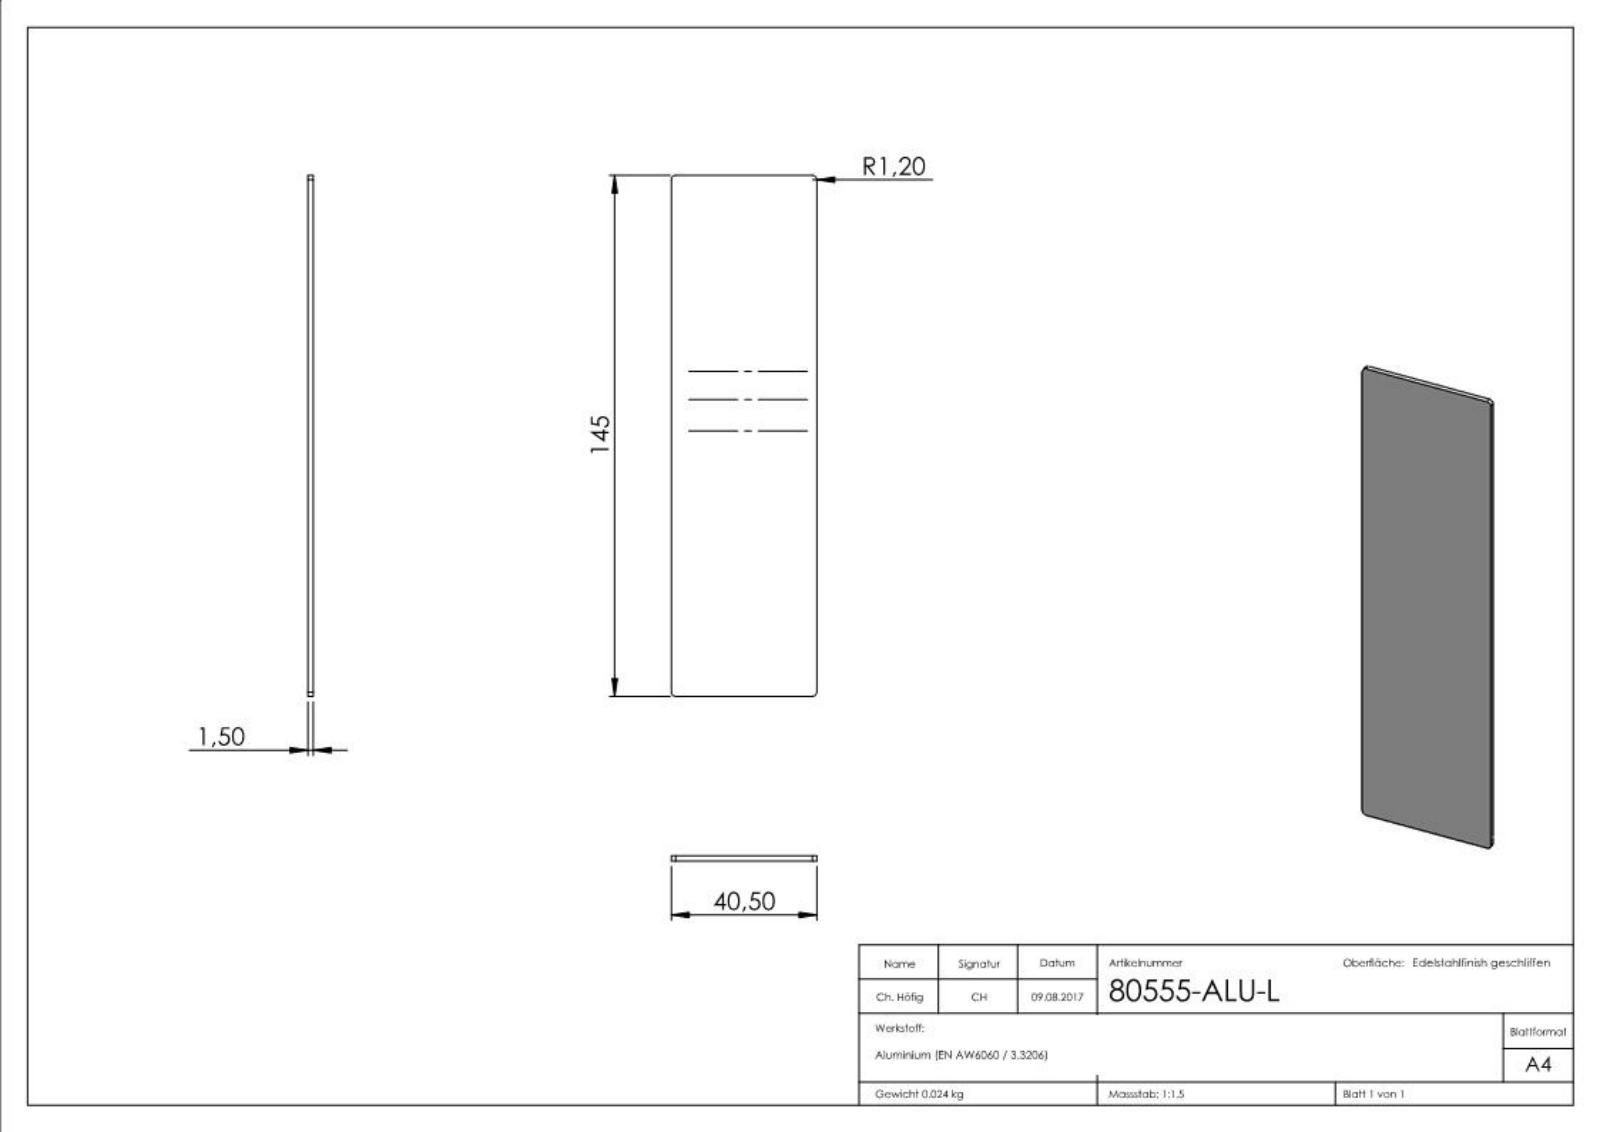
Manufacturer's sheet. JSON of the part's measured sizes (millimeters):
{"part_name": "80555-ALU-L", "step_written_by": "SolidWorks 2015 (CONFIG_CONTROL_DESIGN)", "units": "millimeters", "bodies": {"solids": 1, "faces": 250, "planar": 141, "cylindrical": 4, "other": 105}, "overall_size": [145, 40.5, 1.5], "volume_mm3": 8806, "surface_area_mm2": 12306, "partial_cylinders_radius": [[1.2, 4]], "face_to_face_distances": [1.5, 40.5, 145, 1.4, 2.98, 1.19, 5.62, 2.02, 4.23, 2.64]}
